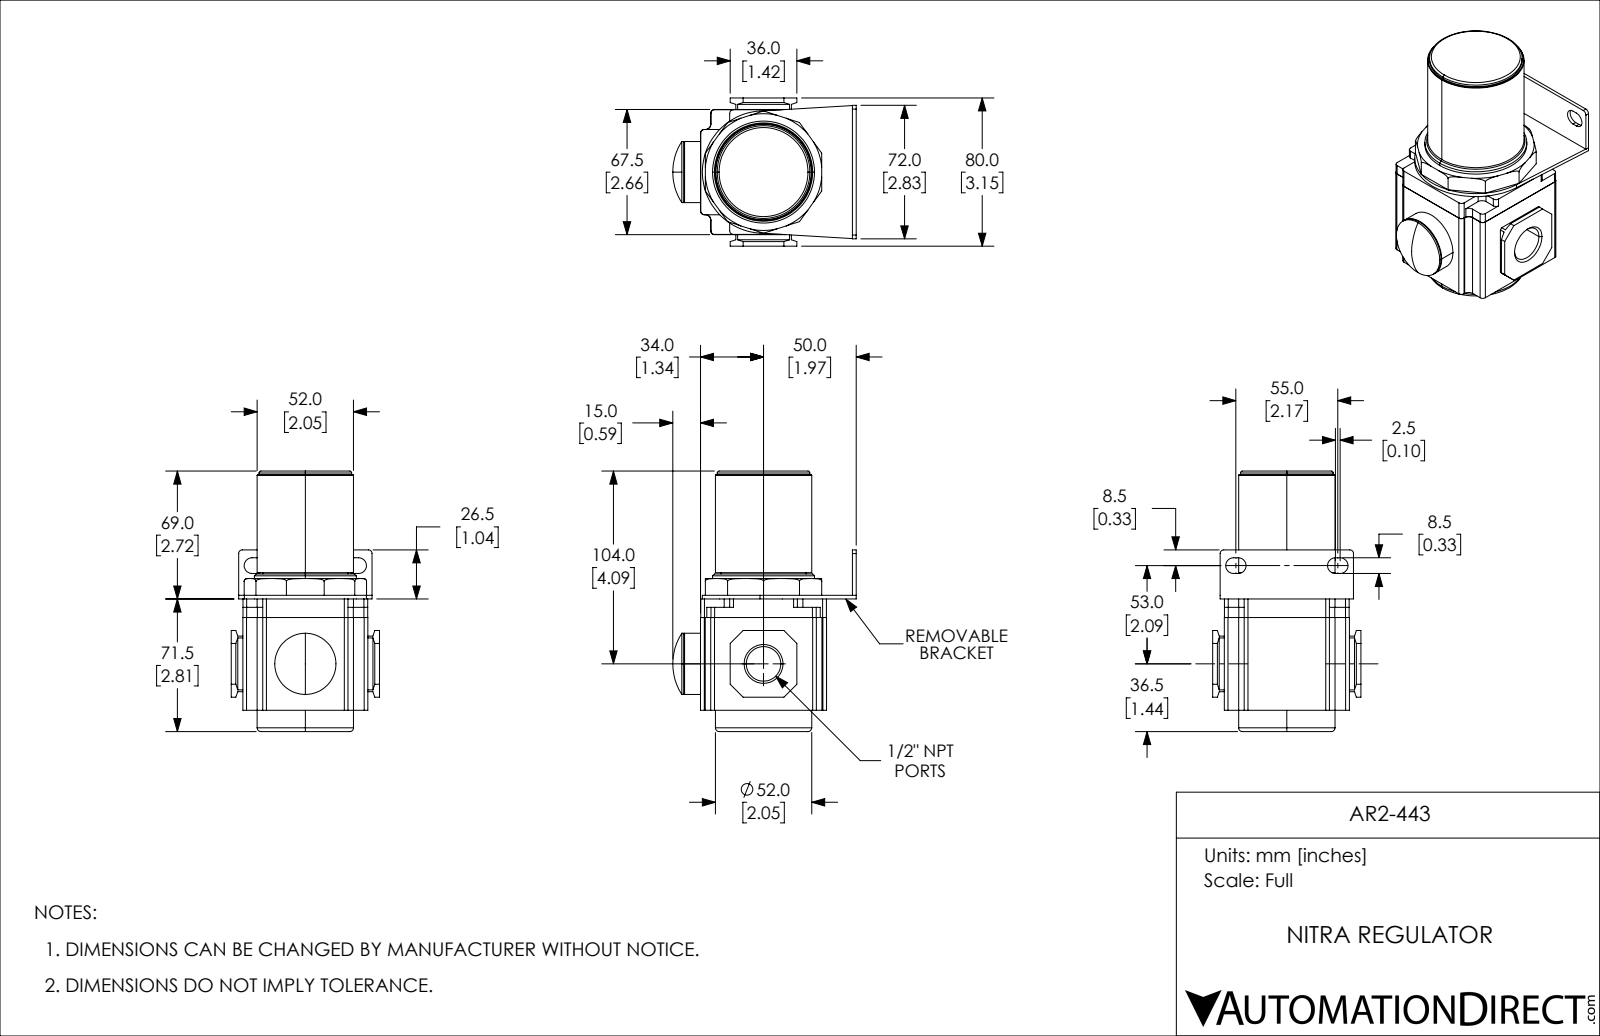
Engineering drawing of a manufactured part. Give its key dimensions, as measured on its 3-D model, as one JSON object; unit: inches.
{"part_name": "AR2-443", "step_written_by": "SolidWorks 2019 (CONFIG_CONTROL_DESIGN)", "units": "inches", "bodies": {"solids": 1, "faces": 192, "planar": 109, "cylindrical": 57, "other": 26}, "overall_size": [5.531, 3.898, 3.15], "volume_in3": 28.13, "surface_area_in2": 79.36, "round_holes": [[0.733, 1]], "round_bosses_or_shafts": [[2.165, 1], [2.047, 1], [1.969, 1], [1.807, 1], [1.299, 1]], "partial_cylinders_radius": [[0.079, 22], [0.118, 12], [0.167, 4], [1.299, 1]], "face_to_face_distances": [0.079, 2.894, 0.453, 2.638, 0.63, 2.815, 2.441, 5.531, 5.079, 2.362]}
